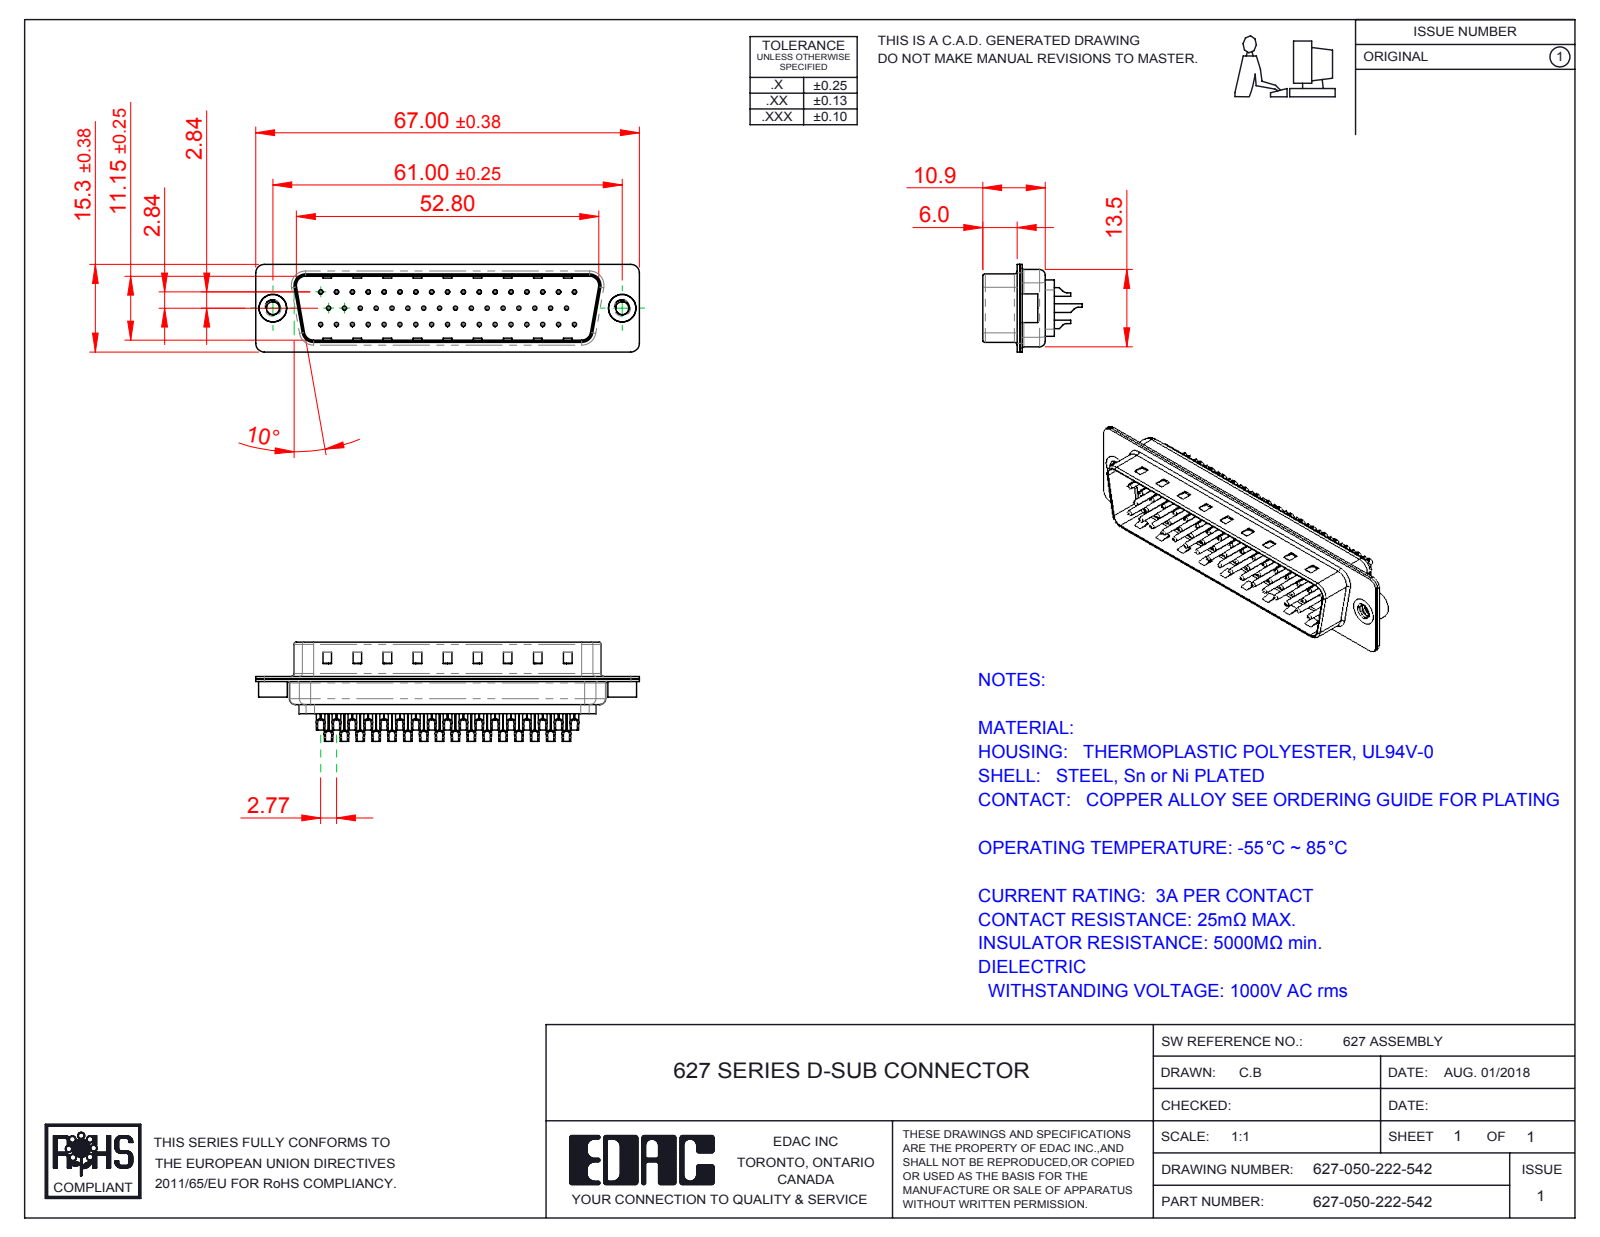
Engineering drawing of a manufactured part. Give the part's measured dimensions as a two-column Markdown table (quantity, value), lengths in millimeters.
| quantity | value |
| --- | --- |
| part name | 627 Housing_50 LP; 627 Contact Row 1_22L; 627 Shell Rear_50 Contacts; 627-050-222-542 (+4 more) |
| STEP written by | SolidWorks 2016 (CONFIG_CONTROL_DESIGN) |
| units | millimeters |
| bodies | 55 solids, 3612 faces (903 planar, 1591 cylindrical, 1118 other) |
| overall size | 67 × 17.35 × 15.3 |
| volume | 4 470 mm³ |
| surface area | 12 965 mm² |
| round holes (diameter × count) | 0.35 × 50, 1.1 × 50, 1.6 × 50, 2.26 × 2, 4 × 2, 4.8 × 2 |
| round bosses / shafts (diameter × count) | 2 × 50, 1.5 × 50, 0.75 × 50, 5 × 2, 4.9 × 2 |
| partial cylindrical surfaces (radius × count) | 1.5 × 16, 2 × 12, 0.5 × 8, 1.6 × 8, 1 × 7, 0.25 × 4, 0.6 × 4, 0.65 × 4 |
| main face-to-face distances | 0.4, 0.45, 11.55, 0.9, 6.05, 6.5, 0.78, 12.33, 1.95, 0.77 |
| hole center spacings | 3.16, 2.77, 5.54, 8.31, 11.08, 13.85, 16.62, 5.03 |
